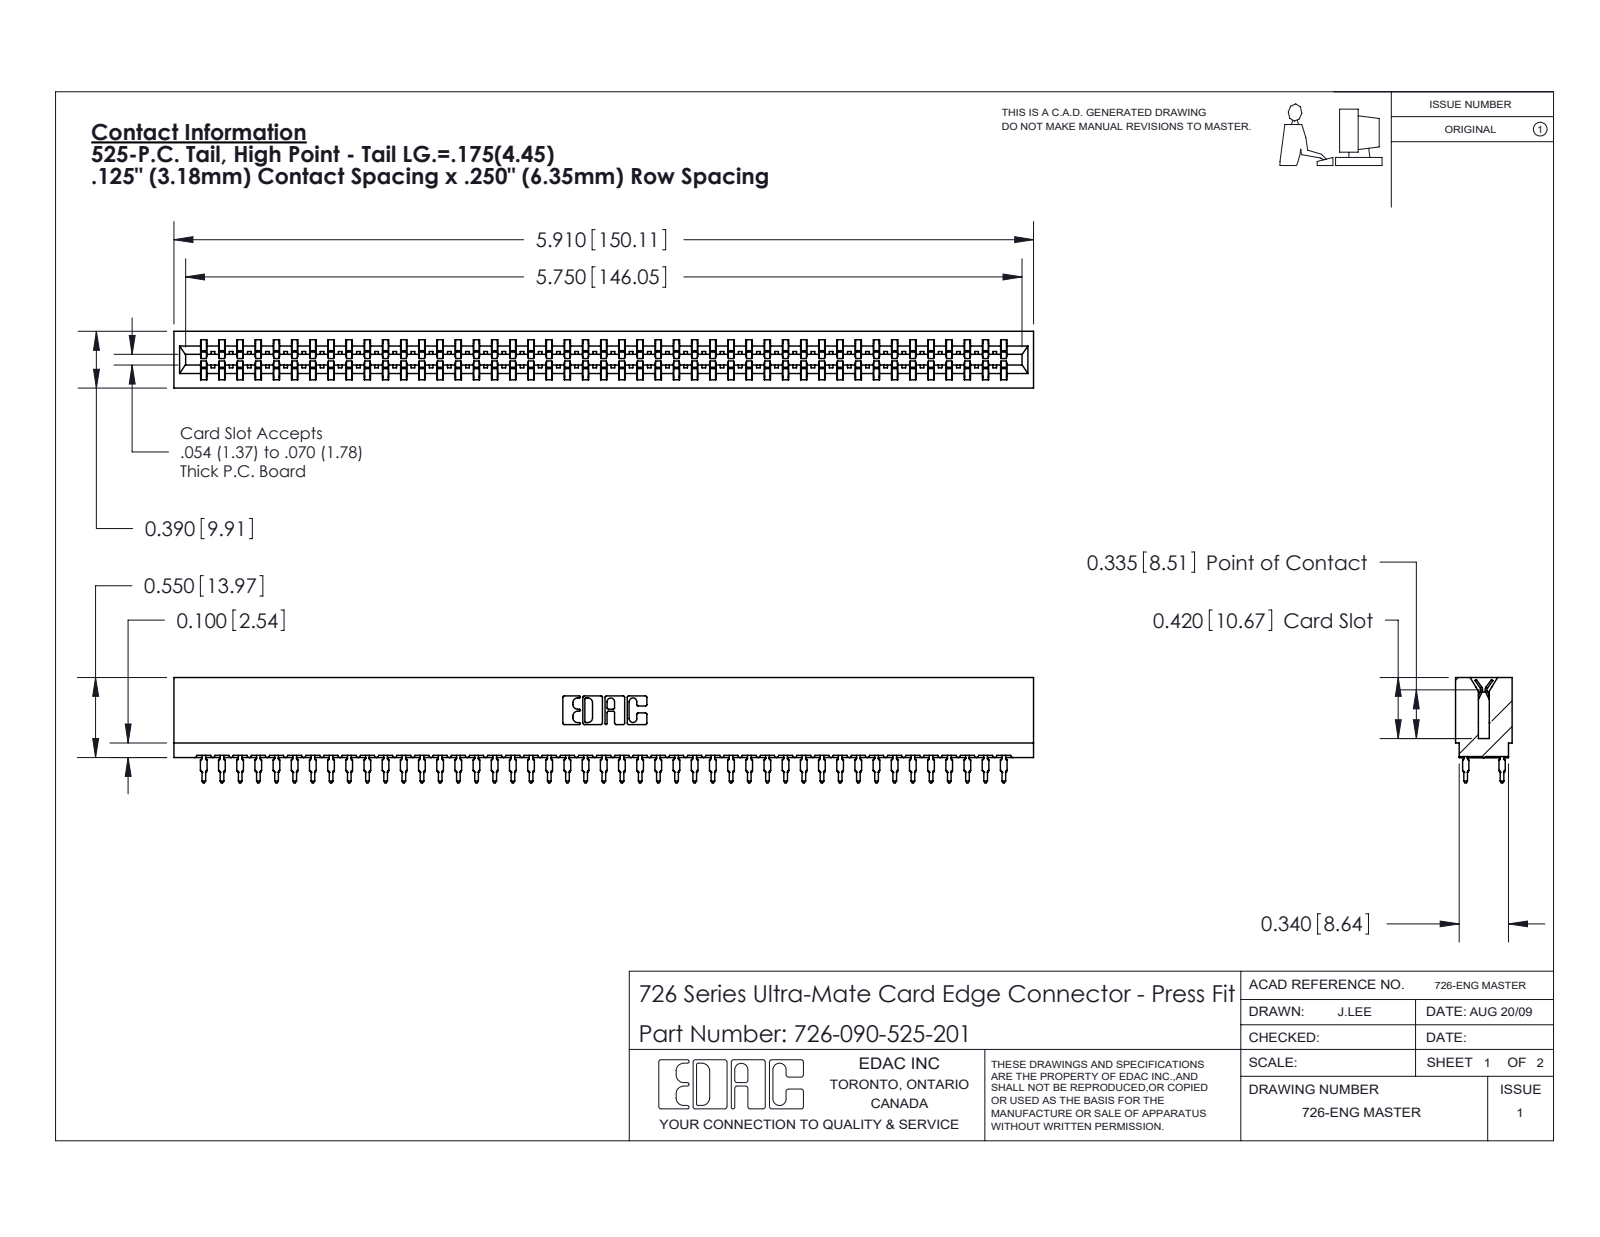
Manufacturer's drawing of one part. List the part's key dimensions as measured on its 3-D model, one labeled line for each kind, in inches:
Part name (STEP PRODUCT): 746-292-001_525; 726-090-525-201; 726 Part_.515 Slot Depth - 01
STEP written by: SolidWorks 2020 (CONFIG_CONTROL_DESIGN)
Units: inches
Bodies: 91 solids, 8152 faces (4195 planar, 1617 cylindrical, 2340 other)
Overall size (bounding box): 5.91 × 0.724 × 0.39
Volume: 0.839 in³ · Surface area: 35.29 in²
Partial cylindrical surfaces — rounded edges, fillets, slot ends (radius × count): R0.021 ×180, R0.015 ×46, R0.01 ×22, R0.005 ×8, R0.011 ×8, R0.007 ×6, R0.031 ×6, R0.026 ×3
Main face-to-face distances: 0.057, 0.333, 0.39, 0.025, 0.307, 0.25, 0.275, 0.083, 0.365, 0.032
